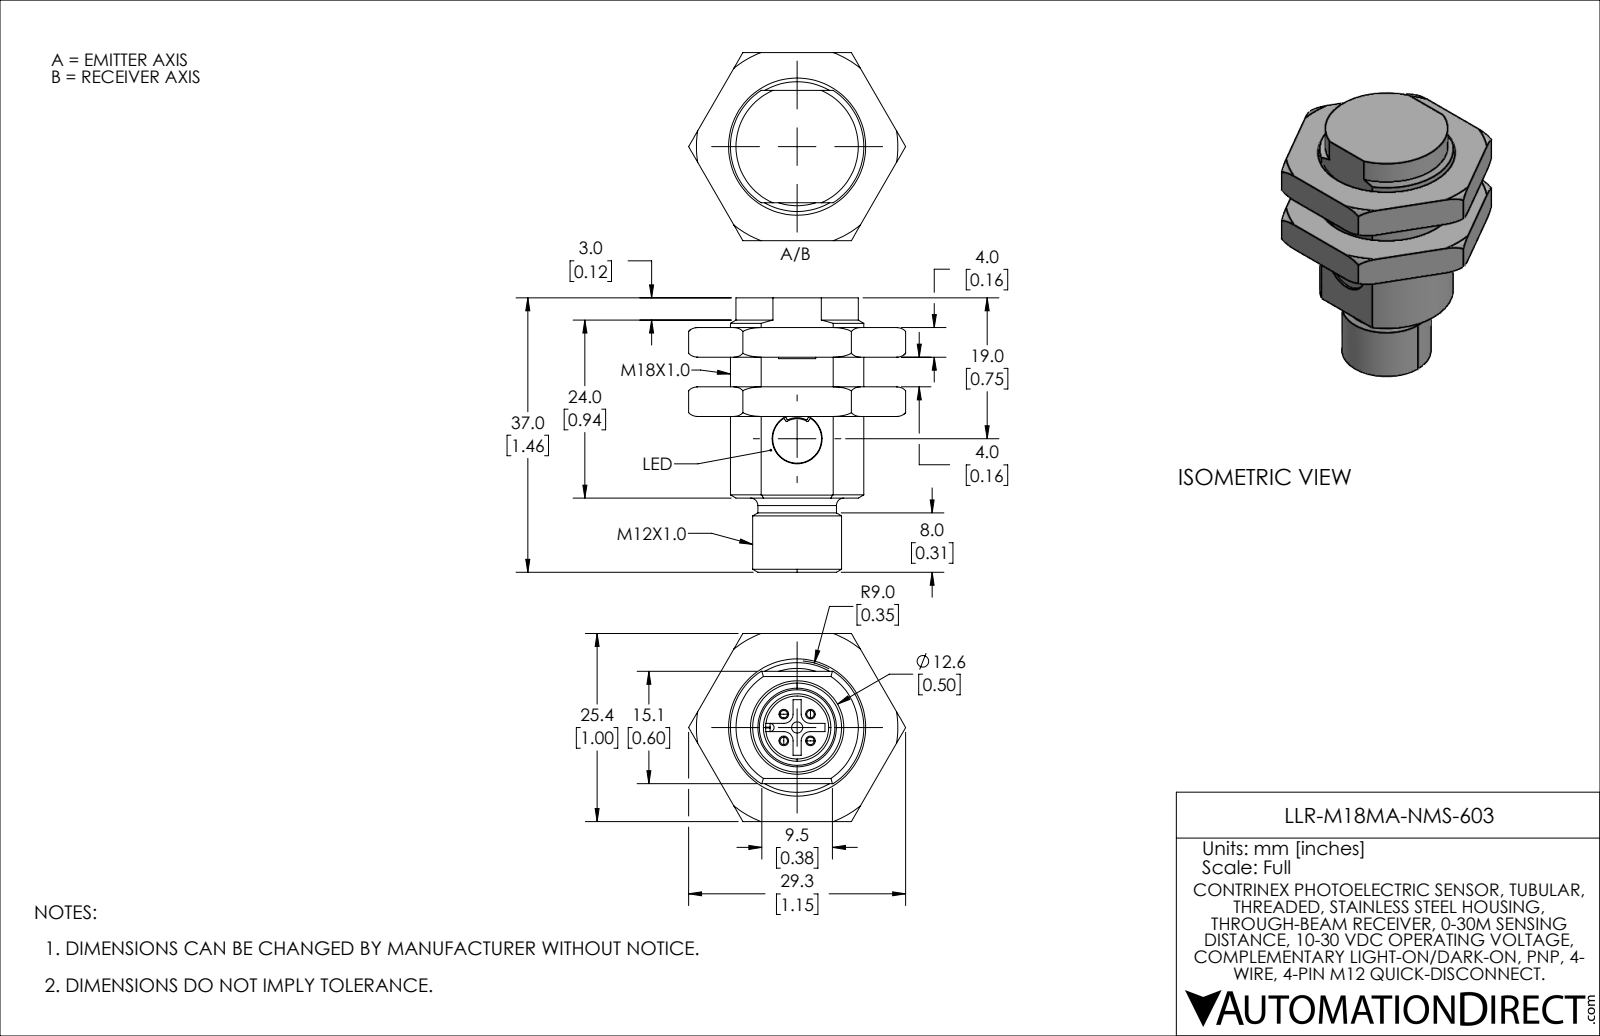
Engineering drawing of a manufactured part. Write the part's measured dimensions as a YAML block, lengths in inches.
part_name: "LLR-M18MA-NMS-603"
step_written_by: "SolidWorks 2021 (AUTOMOTIVE_DESIGN)"
units: inches
bodies: {solids: 3, faces: 176, planar: 65, cylindrical: 50, other: 61}
overall_size: [1.457, 1.153, 0.998]
volume: 0.572
surface_area: 7.737
round_holes:
  - {diameter: 0.059, count: 1}
  - {diameter: 0.266, count: 1}
  - {diameter: 0.335, count: 1}
  - {diameter: 0.689, count: 1}
round_bosses_or_shafts:
  - {diameter: 0.039, count: 4}
  - {diameter: 0.472, count: 1}
  - {diameter: 0.417, count: 1}
partial_cylinders:
  - {radius: 0.004, count: 4}
  - {radius: 0.006, count: 4}
  - {radius: 0.049, count: 4}
  - {radius: 0.02, count: 2}
  - {radius: 0.022, count: 1}
  - {radius: 0.106, count: 1}
  - {radius: 0.112, count: 1}
  - {radius: 0.325, count: 1}
face_to_face_distances: [0.157, 0.315, 0.472, 0.998, 0.201, 0.798, 0.597, 0.63, 0.433, 0.591]
